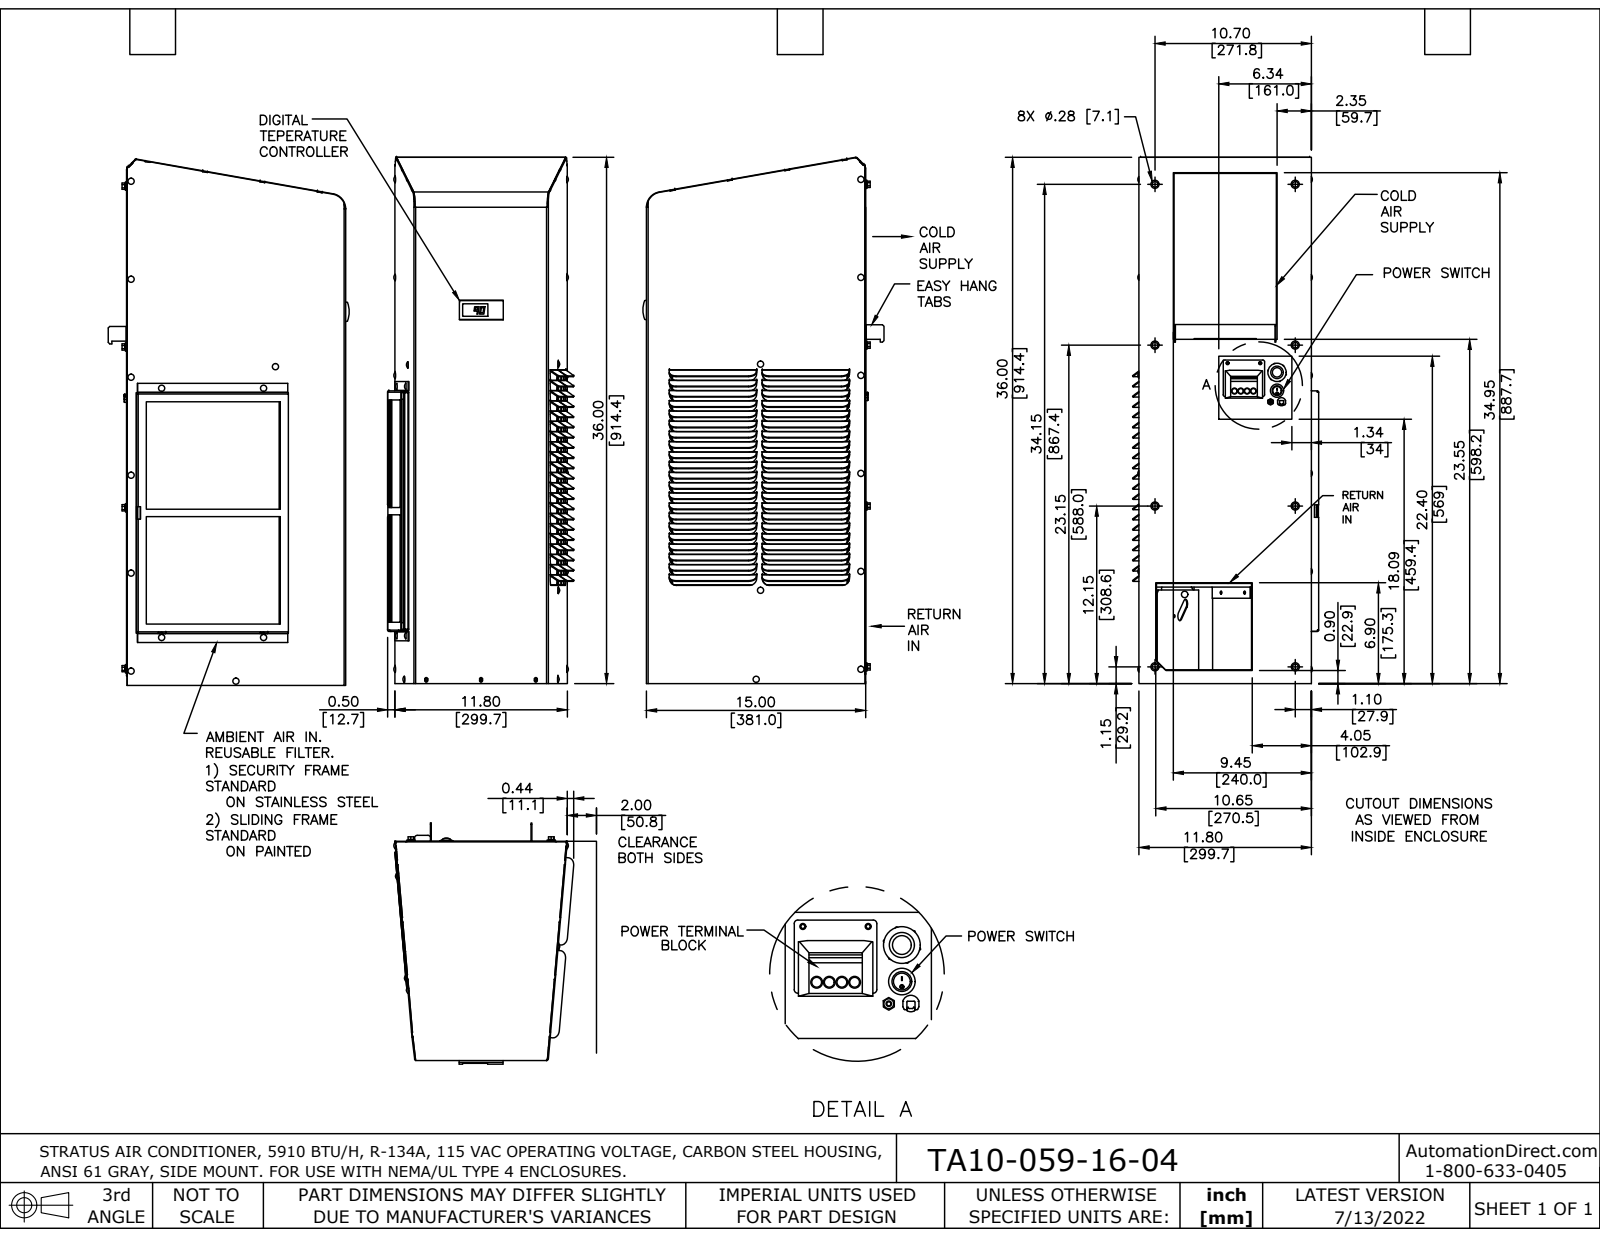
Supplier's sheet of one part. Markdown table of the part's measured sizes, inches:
| quantity | value |
| --- | --- |
| part name | TA10-059-16-04 |
| STEP written by | SolidWorks 2021 (AUTOMOTIVE_DESIGN) |
| units | inches |
| bodies | 40 solids, 3735 faces (2043 planar, 1437 cylindrical, 255 other) |
| overall size | 36.003 × 16.956 × 12.984 |
| volume | 217.2 in³ |
| surface area | 5 520 in² |
| round holes (diameter × count) | 0.194 × 8, 0.25 × 6, 0.277 × 6, 0.228 × 4, 0.082 × 2, 0.091 × 2, 0.204 × 2, 0.201 × 1, 0.21 × 1, 0.375 × 1, 0.64 × 1, 0.7 × 1 |
| round bosses / shafts (diameter × count) | 0.366 × 34, 0.17 × 34, 1.254 × 1, 1.236 × 1, 1.135 × 1, 0.906 × 1, 0.826 × 1, 0.19 × 1 |
| partial cylindrical surfaces (radius × count) | 0.019 × 204, 0.019 × 204, 0.5 × 88, 0.506 × 88, 0.594 × 86, 0.031 × 66, 0.03 × 46, 0.588 × 44 |
| main face-to-face distances | 0.058, 14.937, 14.938, 14.996, 14.994, 0.059, 14.879, 0.036, 0.037, 0.095 |
| hole center spacings | 11, 14.6, 0.024, 6.1, 7, 17.05, 18.431, 22 |
